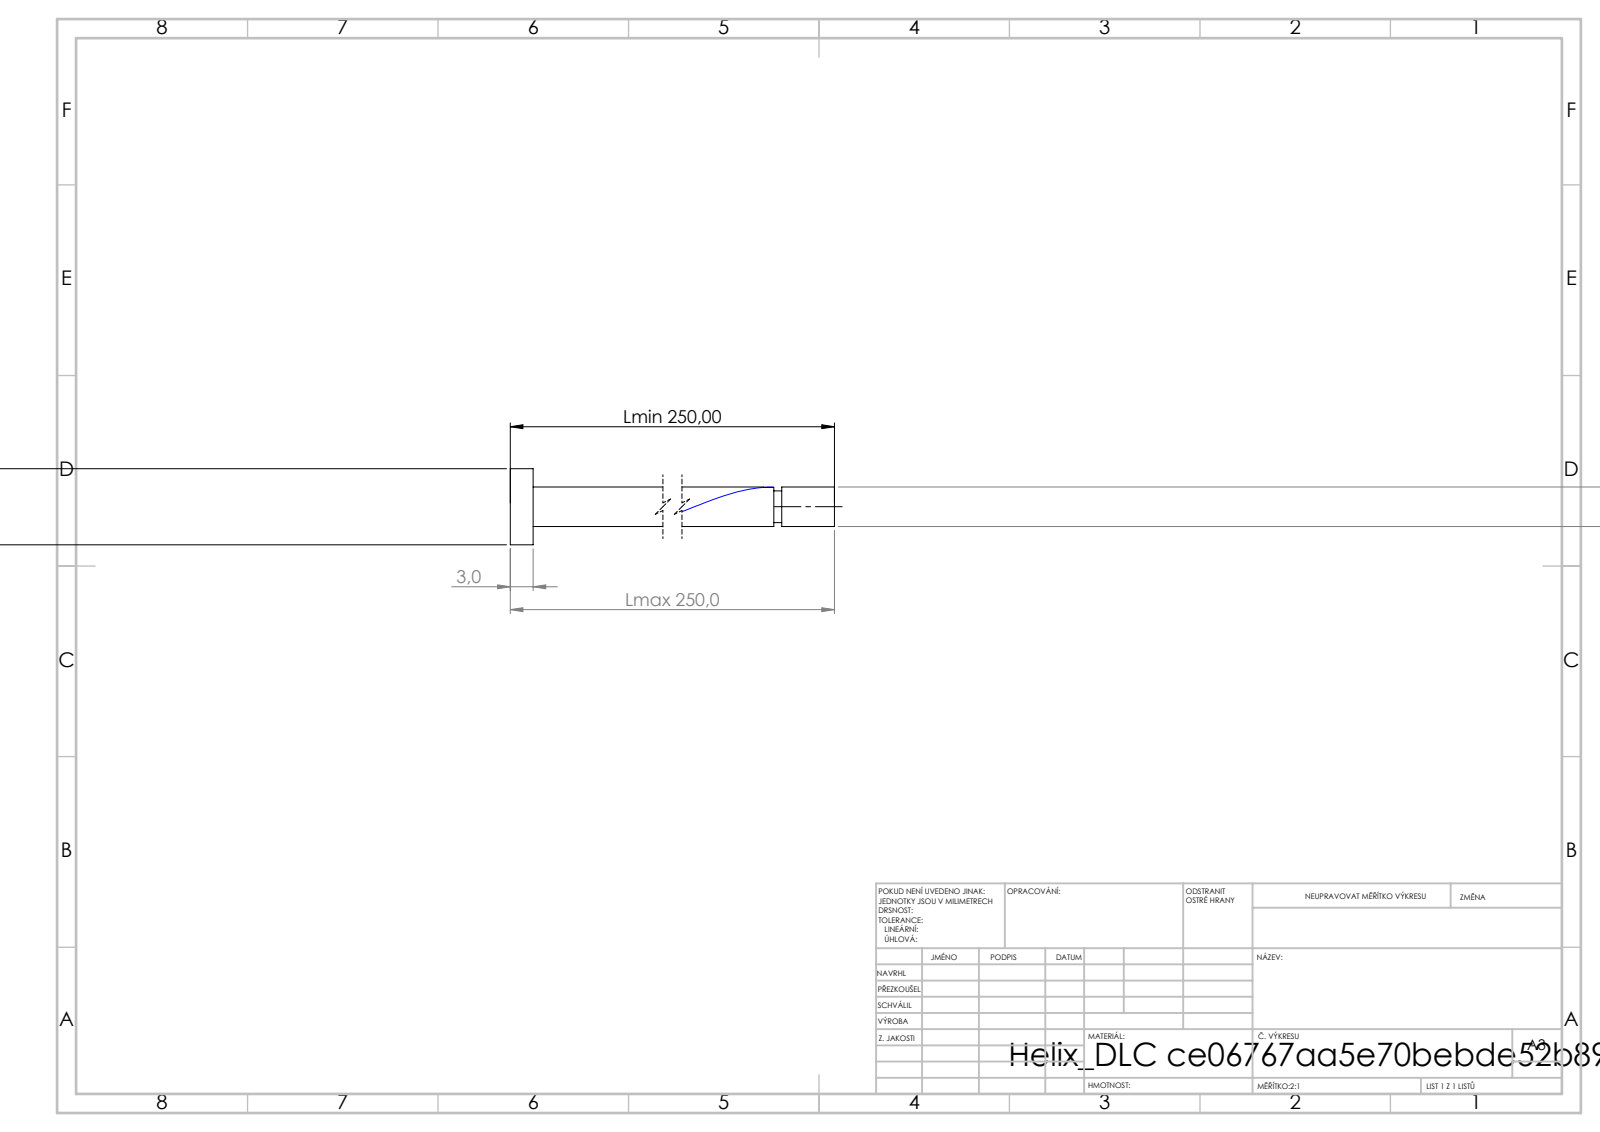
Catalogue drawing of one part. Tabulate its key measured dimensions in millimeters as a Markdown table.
| quantity | value |
| --- | --- |
| STEP written by | SolidWorks 2019 (CONFIG_CONTROL_DESIGN) |
| units | millimeters |
| bodies | 1 solid, 21 faces (6 planar, 14 cylindrical, 1 other) |
| overall size | 250 × 10 × 10 |
| volume | 5 422 mm³ |
| surface area | 4 366 mm² |
| round bosses / shafts (diameter × count) | 10 × 1, 5.2 × 1, 4.16 × 1 |
| main face-to-face distances | 3, 250, 247, 243.09, 240.09, 6.91, 242.05, 239.05, 1.04, 7.95 |
